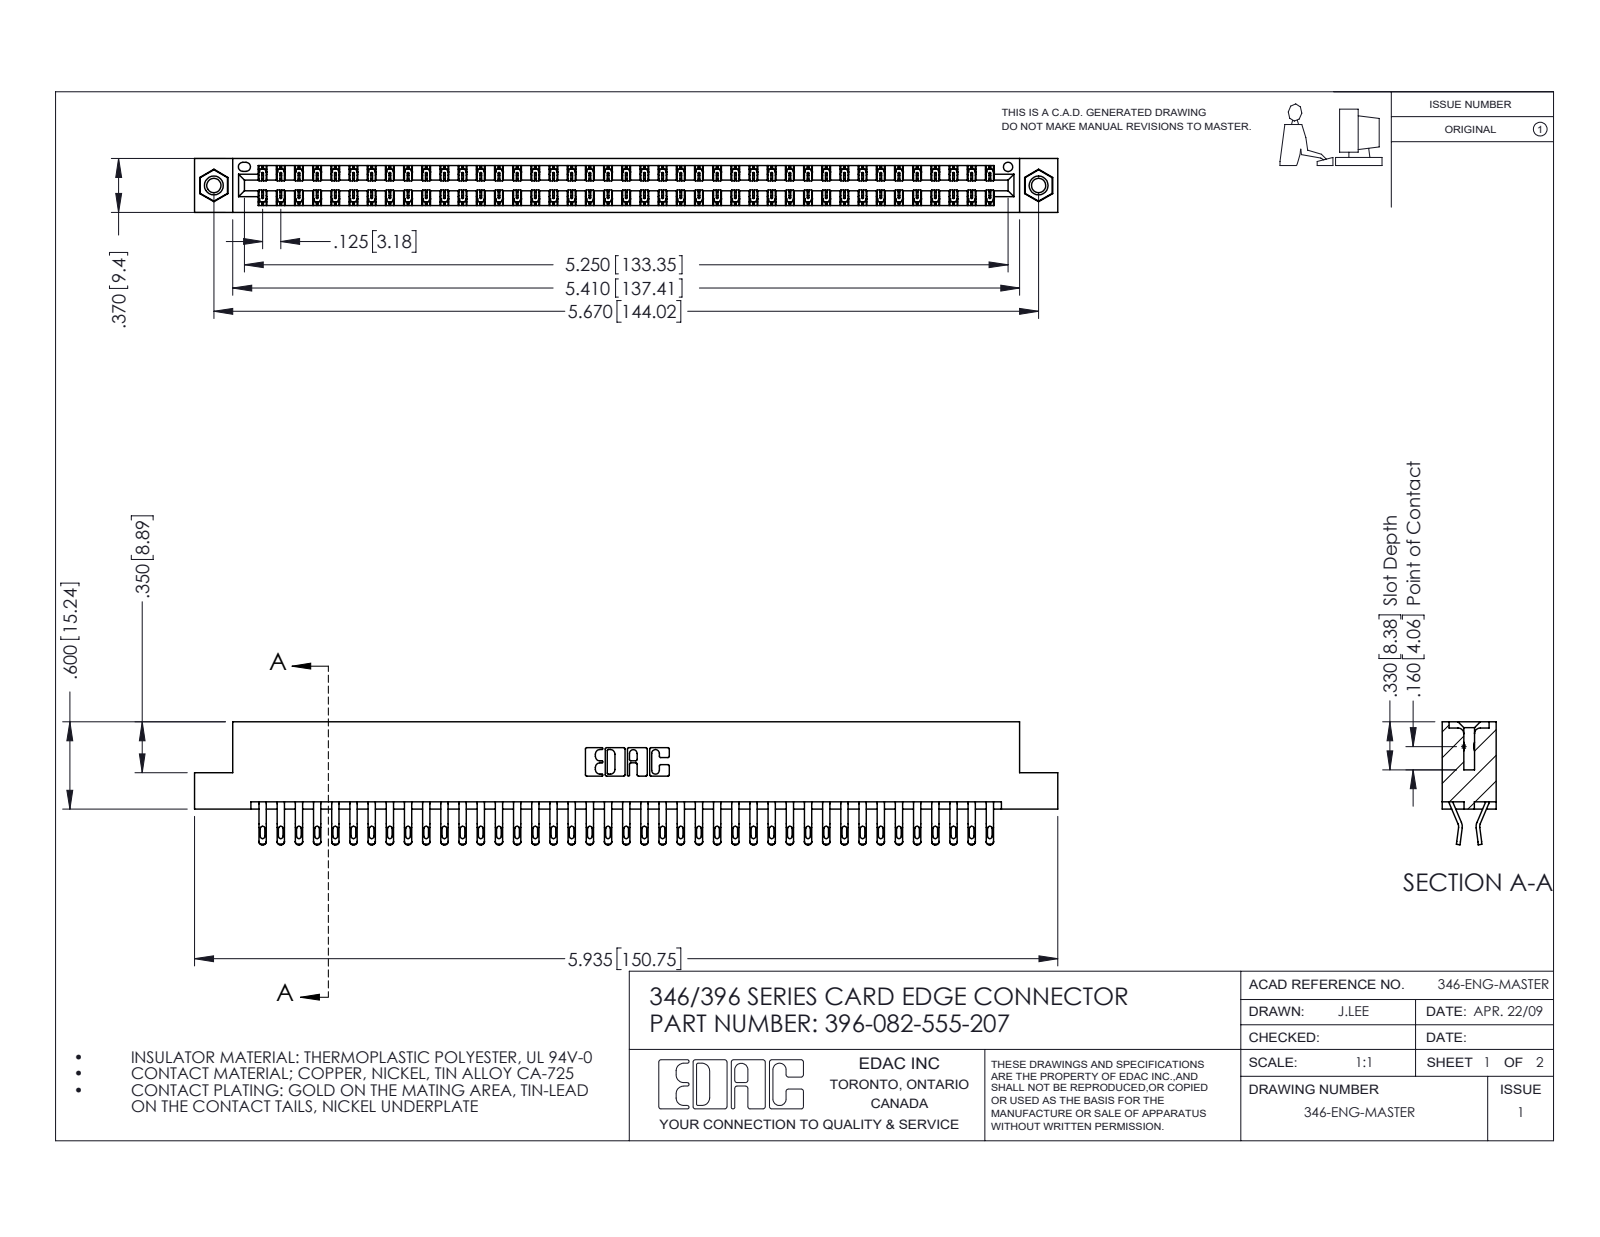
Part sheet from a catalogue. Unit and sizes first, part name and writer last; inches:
Units: inches
Overall size (bounding box): 5.935 × 0.845 × 0.37
Round holes (diameter × count): ⌀0.098 ×2, ⌀0.125 ×2, ⌀0.156 ×2, ⌀0.064 ×1
Round bosses / shafts (diameter × count): ⌀0.155 ×2
Partial cylindrical surfaces — rounded edges, fillets, slot ends (radius × count): R0.016 ×164, R0.02 ×164, R0.006 ×123, R0.01 ×22, R0.007 ×6, R0.031 ×6, R0.026 ×3, R0.01 ×2
Main face-to-face distances: 0.048, 0.322, 0.37, 0.25, 0.025, 0.072, 0.298, 0.275, 0.148, 0.222
Hole centre spacings: 0.246, 5.461, 5.67
Volume: 0.91 in³ · Surface area: 33.12 in²
Bodies: 85 solids, 4938 faces (2814 planar, 2108 cylindrical, 16 other)
Part name (STEP PRODUCT): 396-082-555-207; 346 Part_Flush Mounting Lugs - 0.156 Dia-TI; 345-250-001_345-250-005-103; 345-292-001_555 Tail
STEP written by: SolidWorks 2016 (CONFIG_CONTROL_DESIGN)
